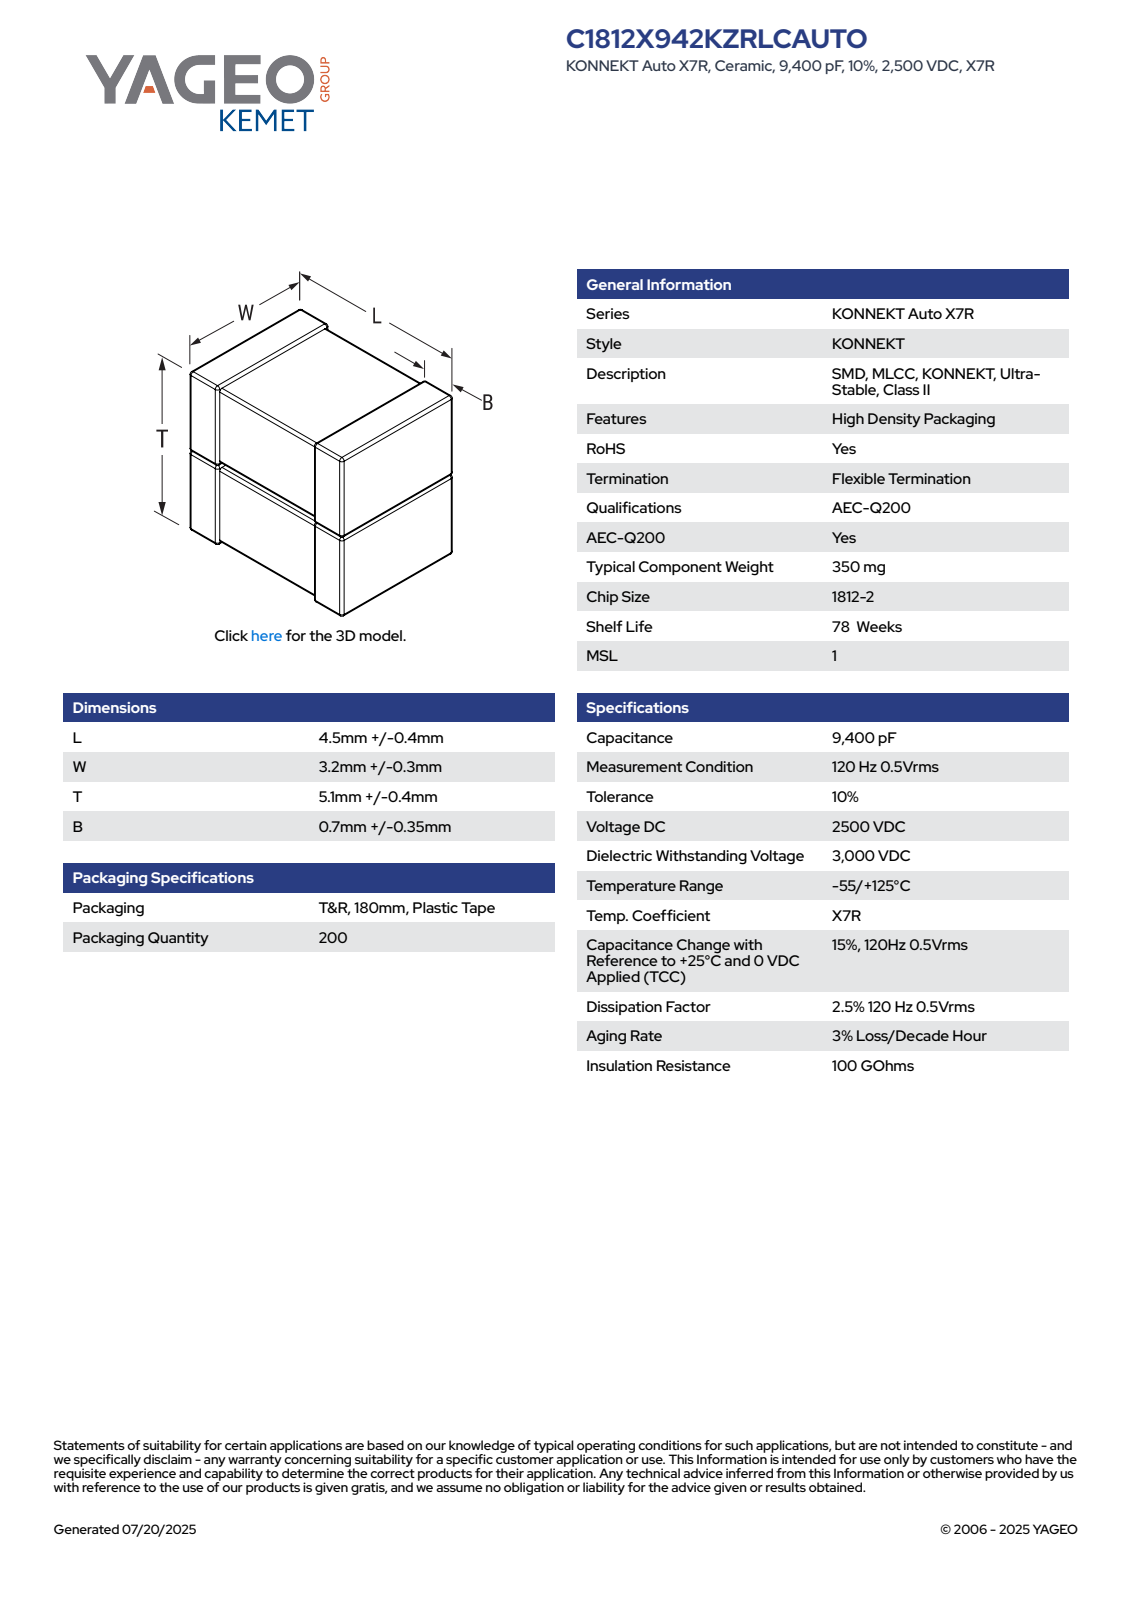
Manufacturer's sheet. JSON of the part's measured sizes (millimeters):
{"part_name": "CCSS_K2T_1812-2_L4.9W3.5B1.05T5.5", "step_written_by": "SolidWorks 2020 (AUTOMOTIVE_DESIGN)", "units": "millimeters", "bodies": {"solids": 4, "faces": 197, "planar": 81, "cylindrical": 84, "other": 32}, "overall_size": [5.5, 4.9, 3.5], "volume_mm3": 89, "surface_area_mm2": 146, "face_to_face_distances": [3.43, 2.61, 2.75, 4.9, 3.36, 2.68, 2.82, 5.43, 3.5, 5.36]}
